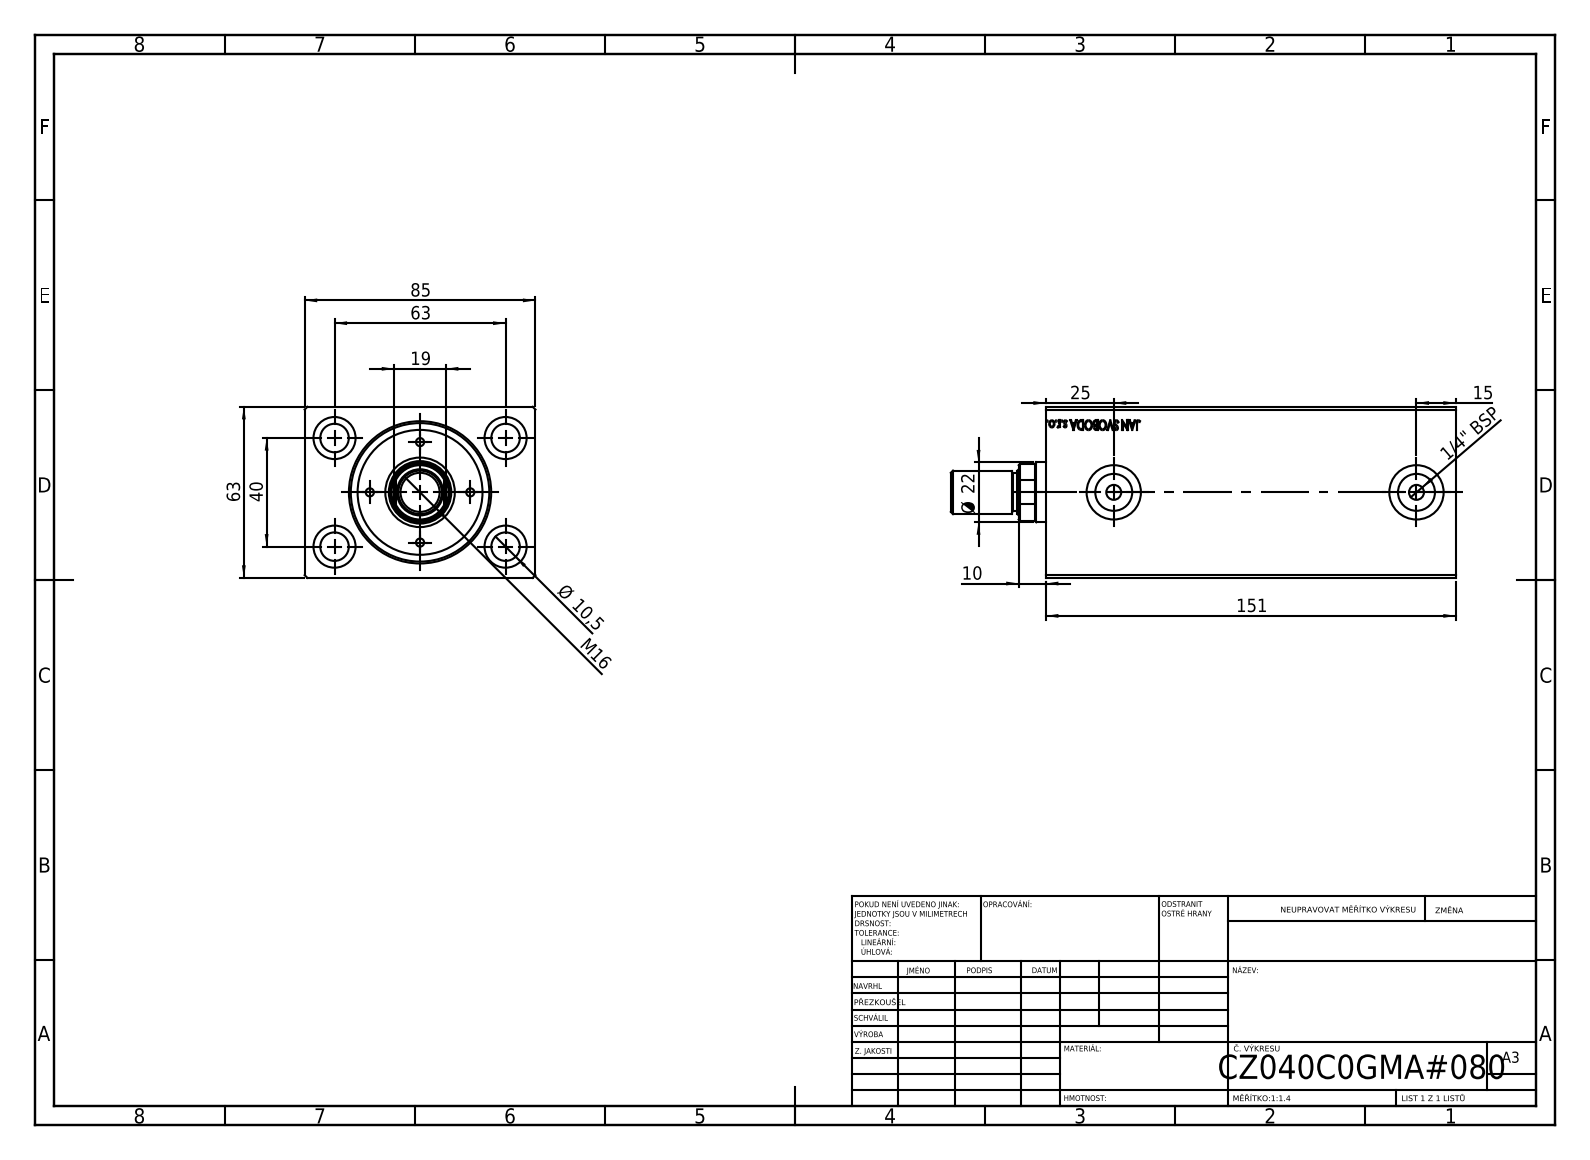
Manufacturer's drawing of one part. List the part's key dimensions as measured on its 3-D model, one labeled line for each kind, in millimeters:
STEP written by: SolidWorks 2019 (CONFIG_CONTROL_DESIGN)
Units: millimetres
Bodies: 1 solid, 825 faces (397 planar, 46 cylindrical, 382 other)
Overall size (bounding box): 151 × 85 × 63
Volume: 564 578 mm³ · Surface area: 94 543 mm²
Round holes (diameter × count): ⌀10.5 ×4, ⌀15.5 ×4, ⌀5.5 ×2, ⌀8 ×2, ⌀13.6 ×2, ⌀20 ×2, ⌀36 ×1, ⌀40 ×1, ⌀51 ×1
Main face-to-face distances: 63, 85, 151, 135.7, 15.3, 150.8, 15.1, 10.33, 140.67, 10
Hole centre spacings: 37.31, 40, 63, 74.63, 91.5, 111.5
